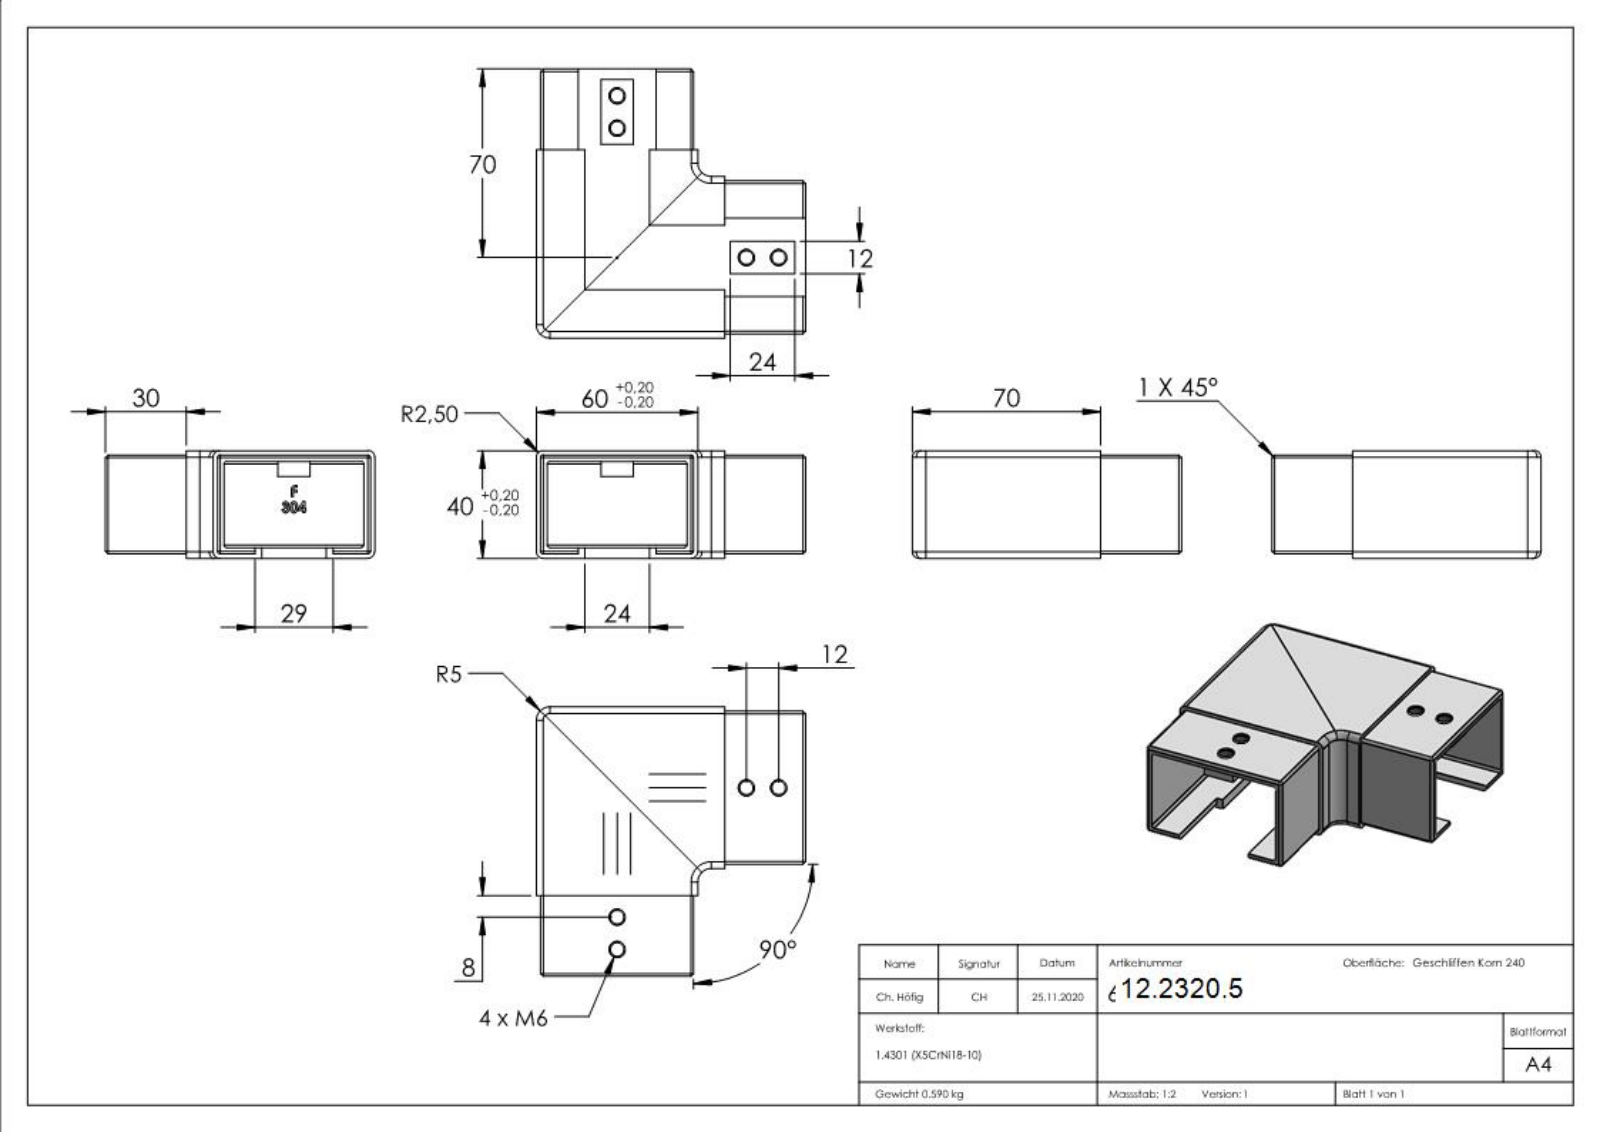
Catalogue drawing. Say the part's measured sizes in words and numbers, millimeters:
The part is named "60358-240". Its 3-D file was written by "SolidWorks 2018 (CONFIG_CONTROL_DESIGN)". It is 1 solid with 421 faces: 210 planar, 34 cylindrical and 177 other. Overall it measures 100 by 100 by 40 millimeters. Its volume is 74 673 cubic millimeters and its surface area 45 722 square millimeters. Round holes: 4 of diameter 5. Partial cylindrical surfaces (rounded edges, fillets, slot ends): 16 of radius 1, 8 of radius 2.5, 2 of radius 5. The main face-to-face distances are 4, 2.4, 1.6, 36, 34.4, 54.4, 38.4, 32, 52, 56. The hole center spacings are 12, 76.84, 67.88, 84.85.
